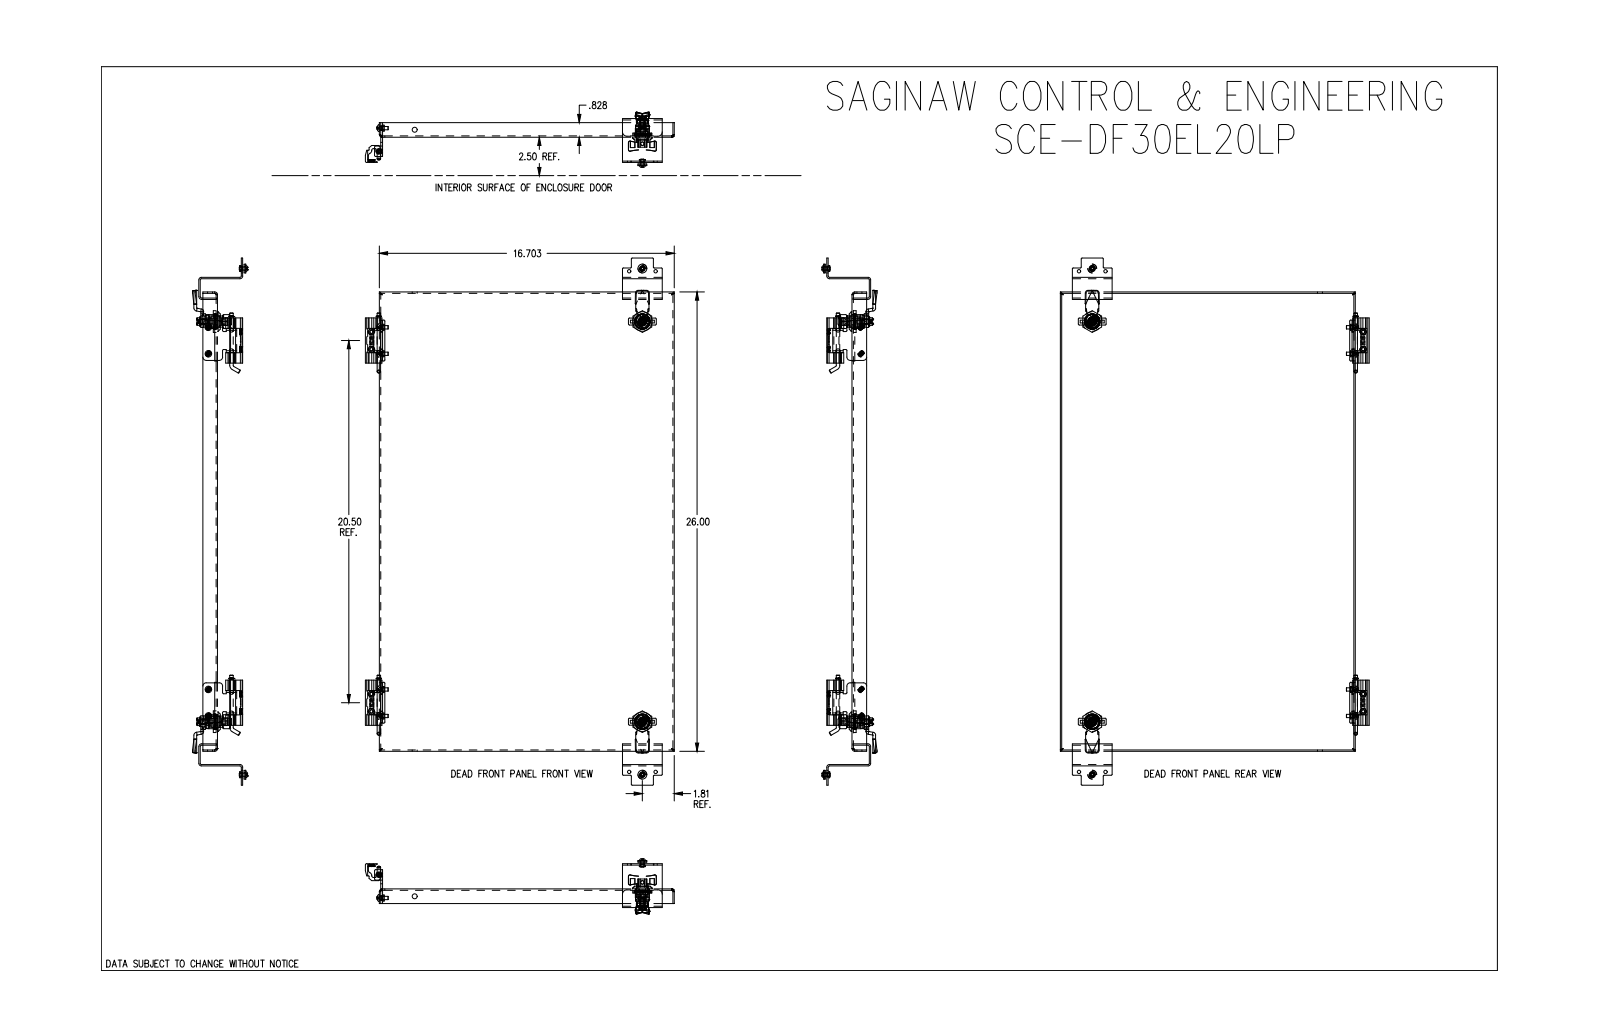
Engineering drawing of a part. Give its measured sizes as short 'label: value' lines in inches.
name: SCE-DF30EL20LP
written by: SolidWorks 2021 (AUTOMOTIVE_DESIGN)
unit: in
bodies: 37 solids, 1183 faces (611 planar, 314 cylindrical, 258 other)
size: 29.838 × 17.494 × 3.119
volume: 36.79 in³; area: 1 147 in²
holes: 6× ⌀0.19, 6× ⌀0.25, 4× ⌀0.17, 4× ⌀0.188, 4× ⌀0.21, 2× ⌀0.197, 2× ⌀0.249, 2× ⌀0.394, 2× ⌀0.433, 2× ⌀0.634, 1× ⌀0.222
bosses: 6× ⌀0.34, 4× ⌀0.373, 4× ⌀0.249, 4× ⌀0.188, 3× ⌀0.196, 2× ⌀1.102, 2× ⌀0.78, 2× ⌀0.63
rounds: 16× R0.157, 13× R0.05, 9× R0.06, 8× R0.059, 8× R0.079, 6× R0.068, 5× R0.063, 5× R0.104
face distances: 0.06, 0.06, 16.643, 25.94, 0.078, 16.703, 16.583, 26, 25.88, 0.827
hole spacings: 0.766, 1.5, 20.5, 25.504, 28.504, 2.942, 0.984, 3
